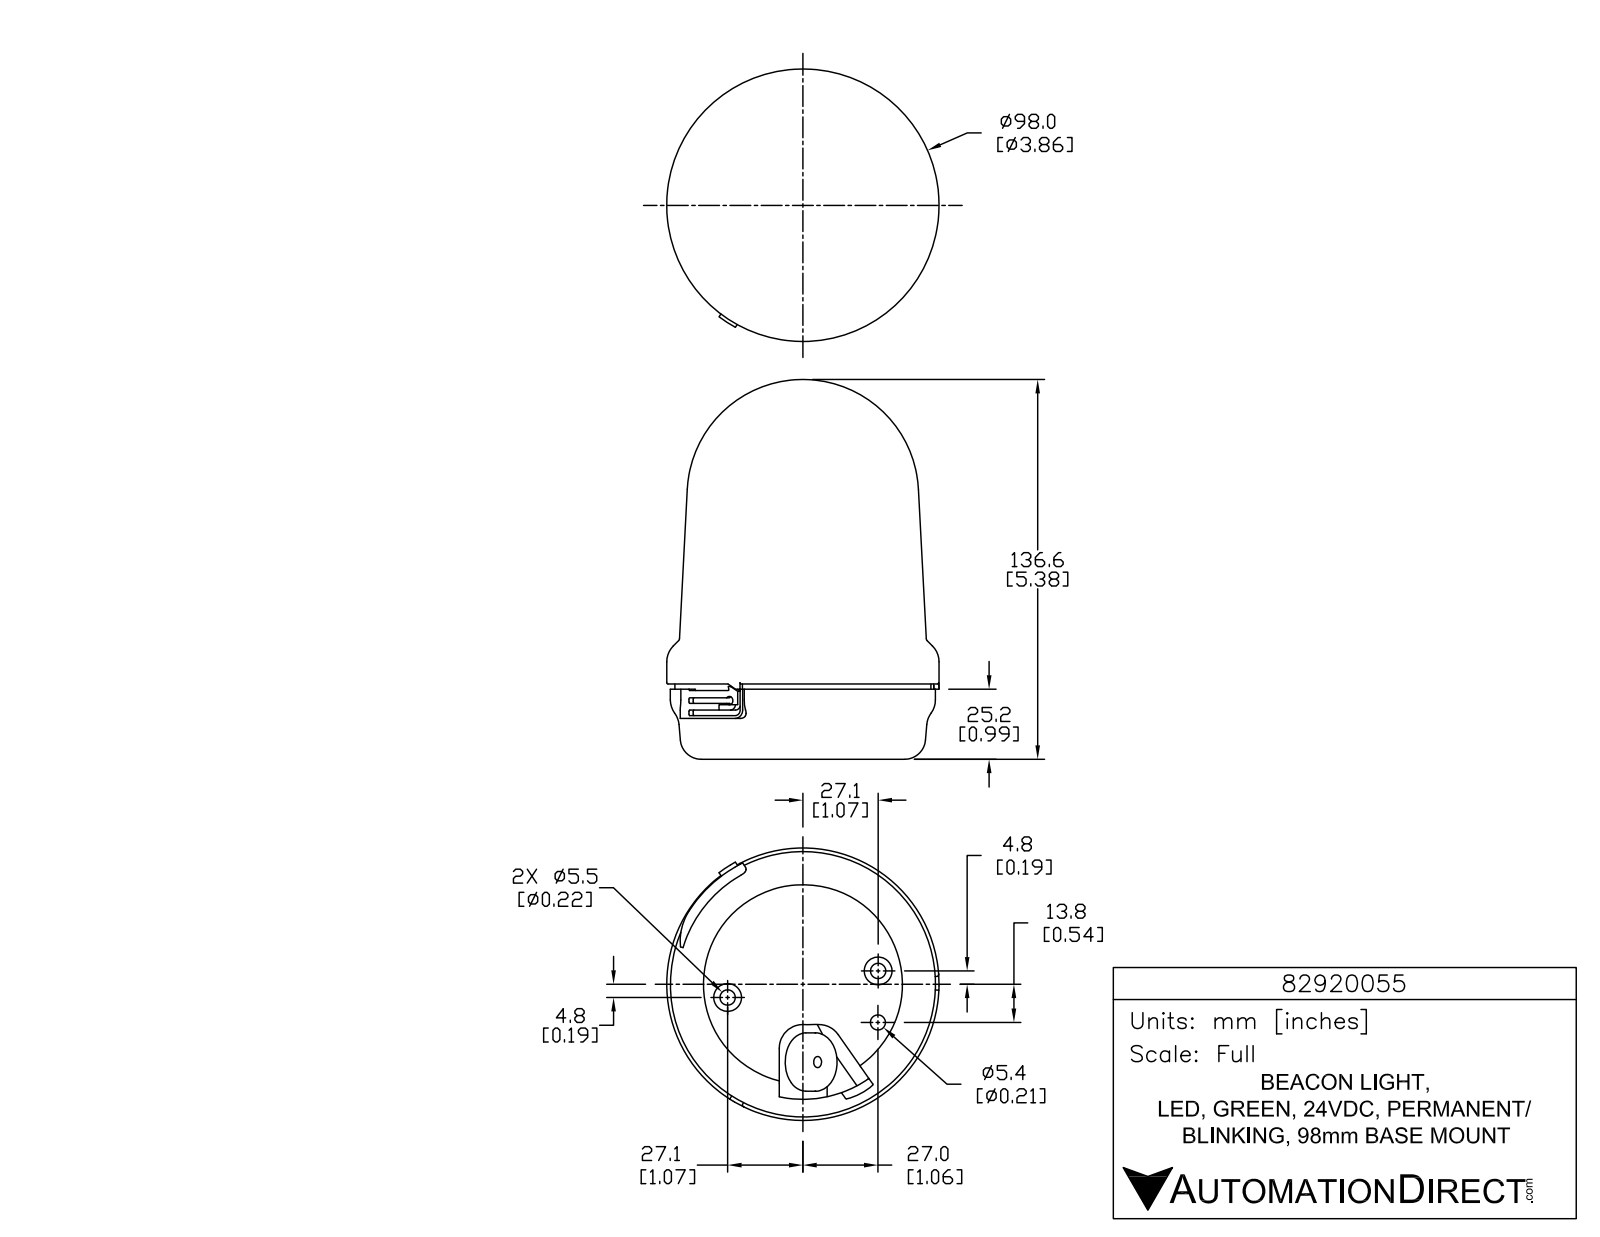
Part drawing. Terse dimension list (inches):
name: 82920055
written by: SolidWorks 2015 (AUTOMOTIVE_DESIGN)
unit: in
bodies: 1 solid, 872 faces (566 planar, 204 cylindrical, 102 other)
size: 5.378 × 3.858 × 3.858
volume: 44.69 in³; area: 73.66 in²
holes: 3× ⌀0.059, 2× ⌀0.217, 1× ⌀0.157, 1× ⌀0.213, 1× ⌀2.819
bosses: 3× ⌀0.339, 3× ⌀0.084, 2× ⌀0.394, 1× ⌀3.858, 1× ⌀3.756, 1× ⌀3.626, 1× ⌀0.827
rounds: 9× R0.005, 6× R0.005, 6× R0.012, 6× R0.012, 6× R0.012, 6× R0.196, 5× R0.02, 4× R0.039
face distances: 1.045, 0.972, 0.073, 0.02, 0.992, 1.065, 0.236, 0.579, 0.559, 0.413
hole spacings: 1.083, 0.73, 1.193, 2.158, 2.165
